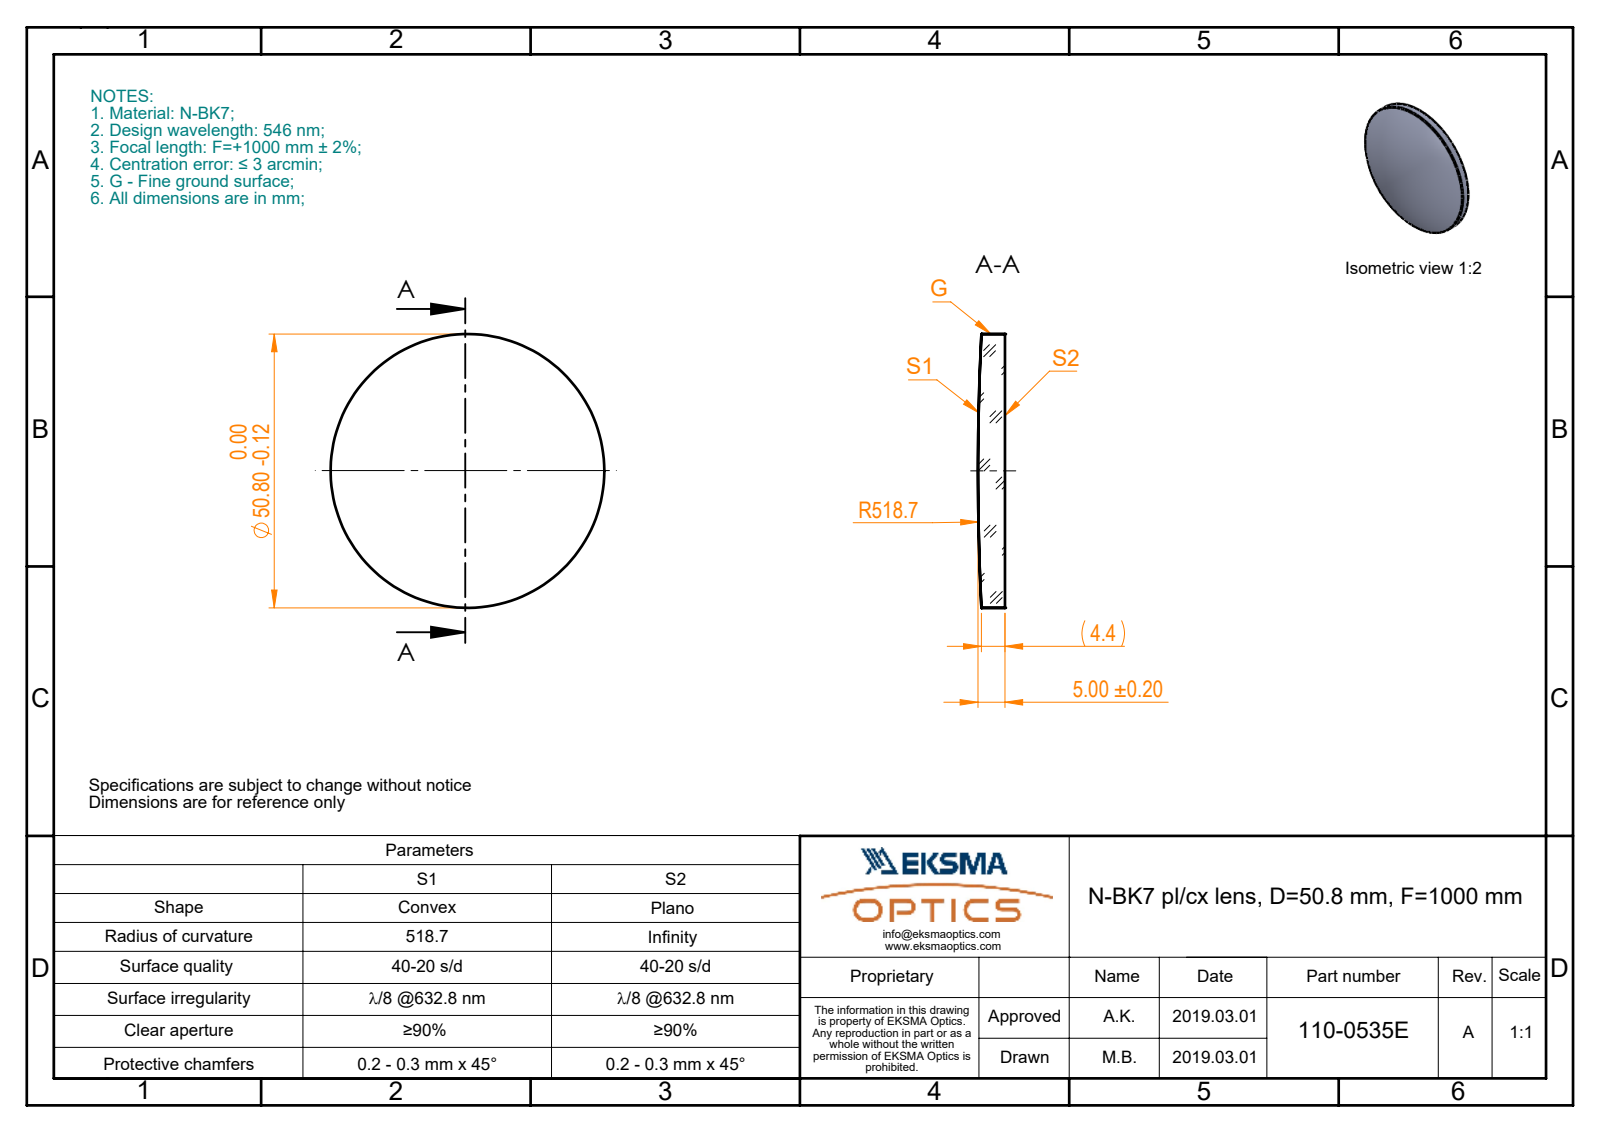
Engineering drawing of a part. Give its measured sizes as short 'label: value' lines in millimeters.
name: 110-0535E BK7 pl-cx 50.8 F1000
written by: SolidWorks 2017 (CONFIG_CONTROL_DESIGN)
unit: mm
bodies: 1 solid, 5 faces (1 planar, 2 cylindrical, 2 other)
size: 50.8 × 50.8 × 5
volume: 9 504 mm³; area: 4 754 mm²
bosses: 1× ⌀50.8
